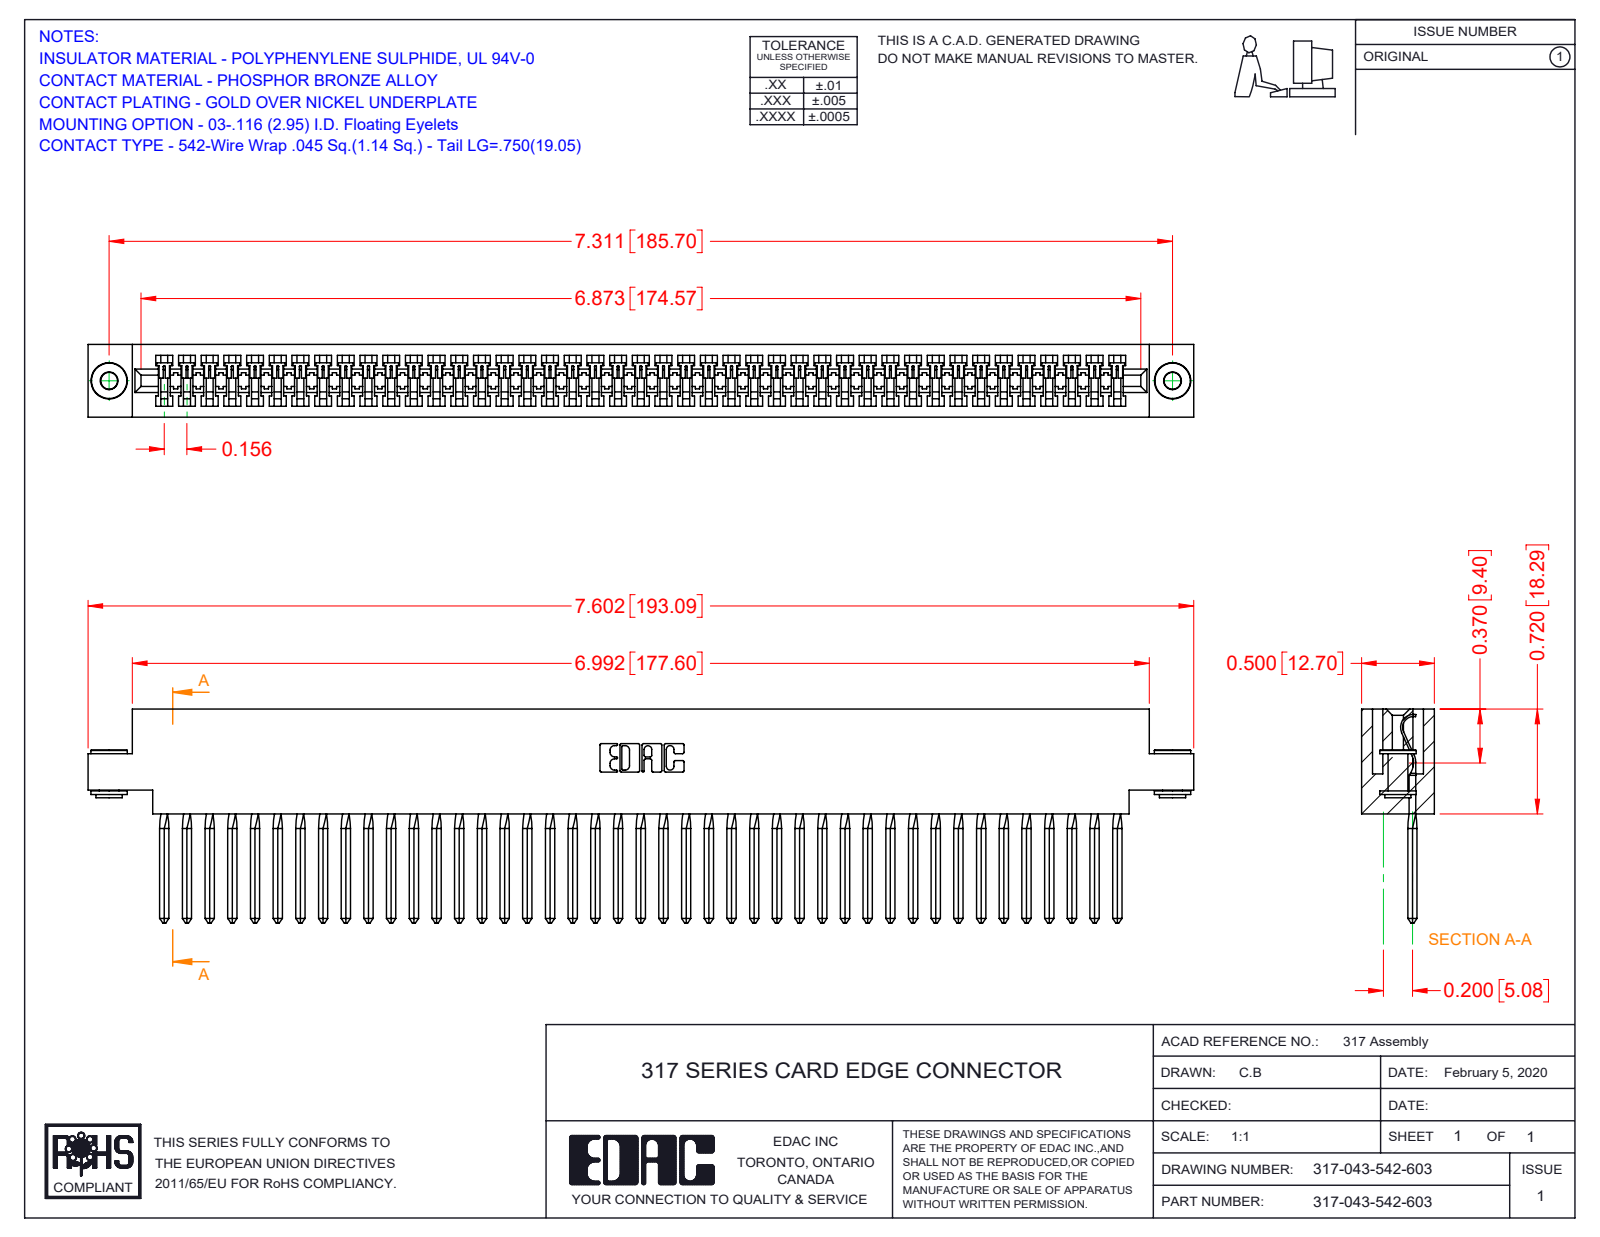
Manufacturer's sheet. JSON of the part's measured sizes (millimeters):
{"part_name": "317-043-542-603; 317-290-003_542; 345-250-002_345-250-002-102; 317 Part_.156 Dia - TH", "step_written_by": "SolidWorks 2016 (CONFIG_CONTROL_DESIGN)", "units": "millimeters", "bodies": {"solids": 46, "faces": 3365, "planar": 2820, "cylindrical": 365, "other": 180}, "overall_size": [193.1, 37.3, 12.7], "volume_mm3": 29870, "surface_area_mm2": 36680, "round_holes": [[2.9, 2], [4, 2]], "round_bosses_or_shafts": [[6.4, 2], [4.6, 2], [3.5, 2]], "partial_cylinders_radius": [[0.2, 86], [0.3, 22], [0.2, 6], [0.8, 6], [0.7, 3], [1.9, 1], [2.3, 1], [2.5, 1]], "face_to_face_distances": [12.7, 1.9, 10.8, 8.9, 18.3, 3.5, 5, 5.4, 7.3, 5.4], "hole_center_spacings": [185.7]}
